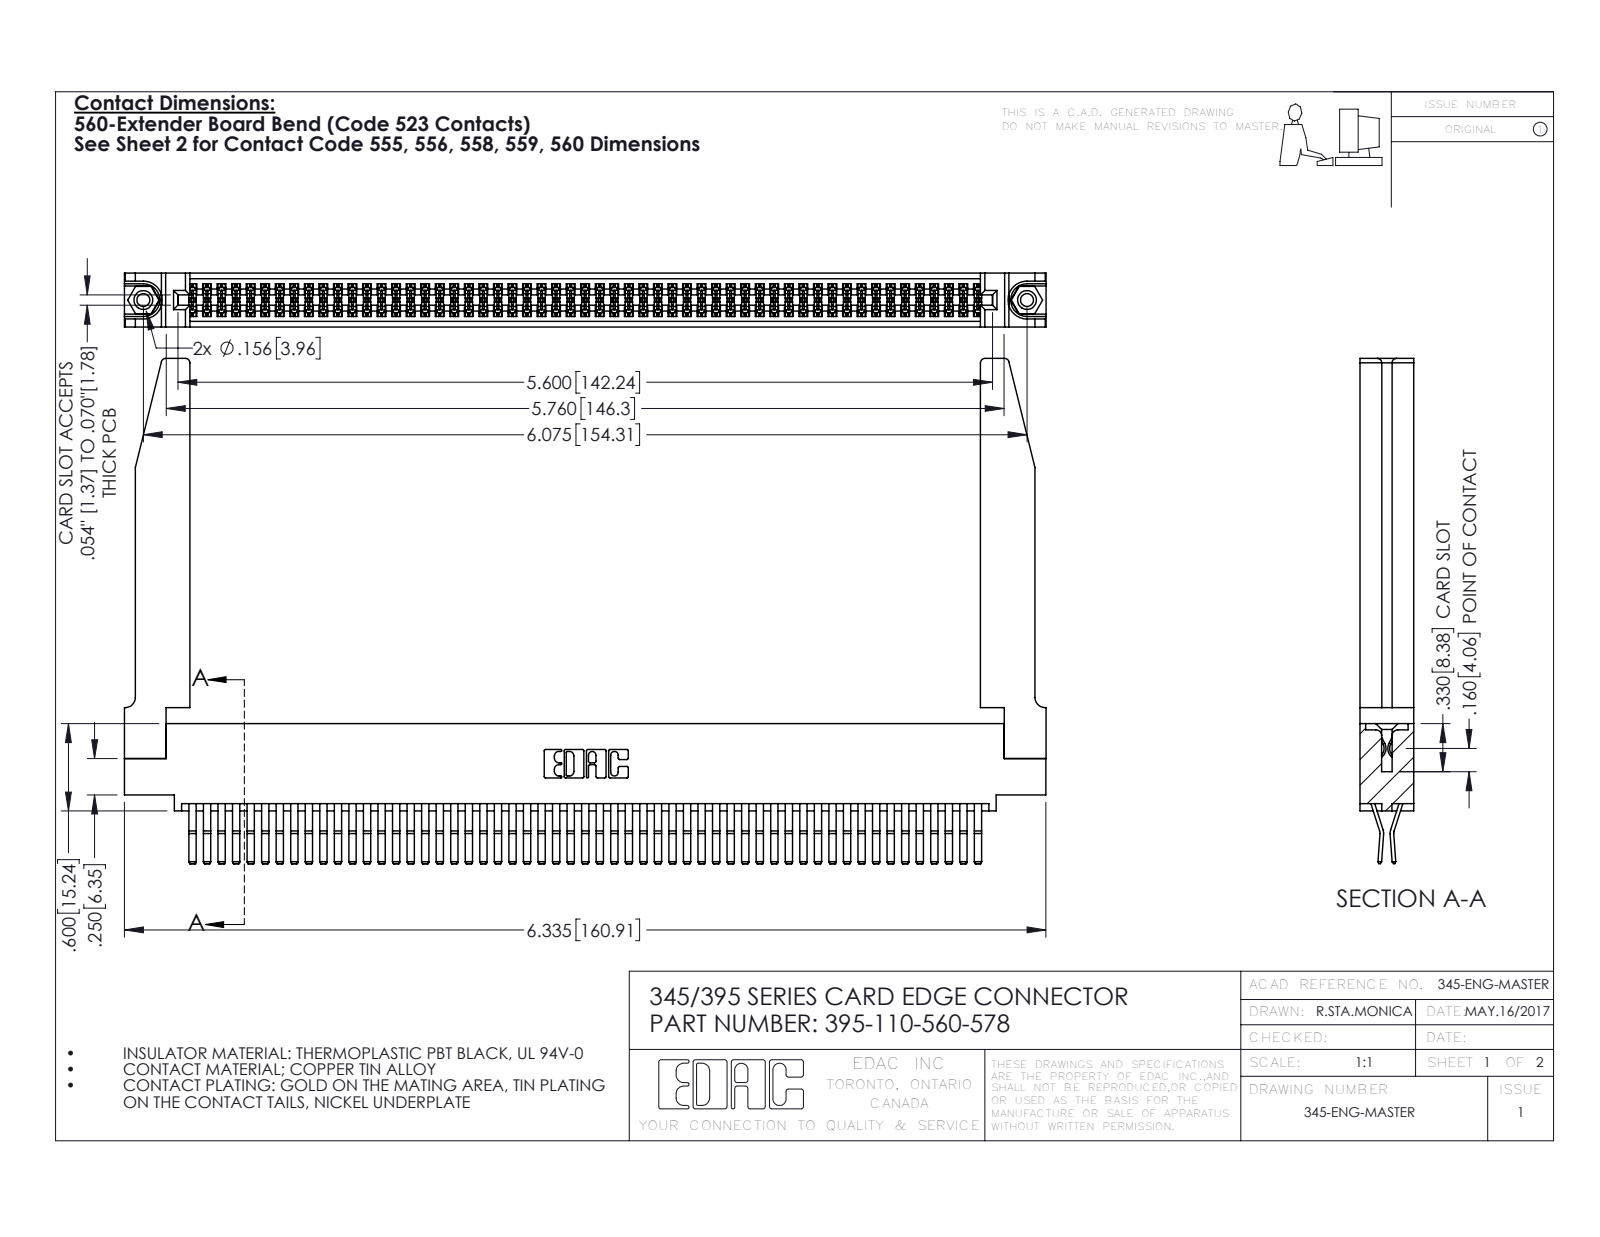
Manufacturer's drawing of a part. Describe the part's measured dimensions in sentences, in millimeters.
The part is named "345-250-001_345-250-001-102; 345-220-078_345-220-078; 395-110-560-578; 345-292-001_560 Tail (+1 more)". Its 3-D file was written by "SolidWorks 2016 (CONFIG_CONTROL_DESIGN)". It is 115 solids with 6084 faces: 3856 planar, 2176 cylindrical and 52 other. Overall it measures 160.9 by 88.2 by 9.4 millimeters. Its volume is 24 170 cubic millimeters and its surface area 33 280 square millimeters. Round holes: 2 of diameter 2.3, 2 of diameter 3.2, 2 of diameter 4, 1 of diameter 1.6. Round bosses or shafts: 2 of diameter 3.9. Partial cylindrical surfaces (rounded edges, fillets, slot ends): 165 of radius 0.2, 22 of radius 0.3, 8 of radius 0.8, 6 of radius 0.2, 6 of radius 0.8, 3 of radius 0.7, 2 of radius 0.3, 2 of radius 0.4. The main face-to-face distances are 1.8, 9.4, 7.6, 0.6, 5.1, 2.5, 6.9, 5.7, 4.4, 3.8. The hole center spacings are 6.9, 148.3, 154.3.
